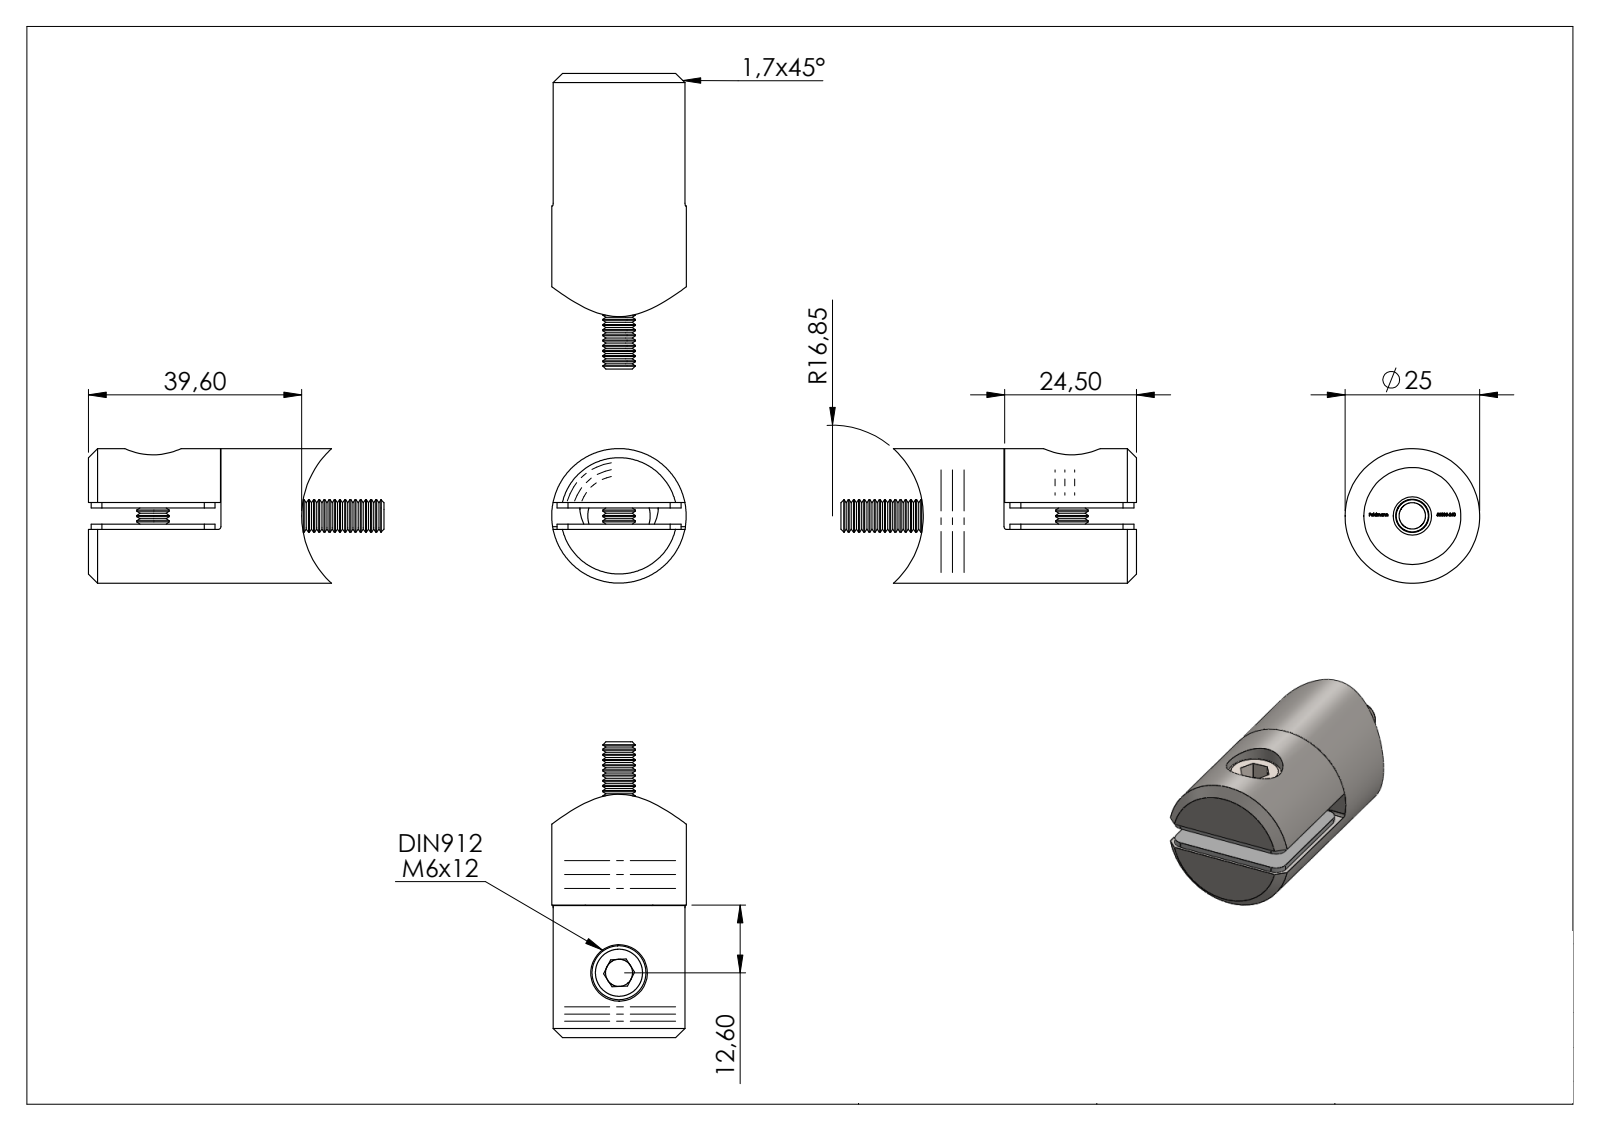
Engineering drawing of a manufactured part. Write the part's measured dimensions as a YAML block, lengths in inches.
part_name: "socket countersunk head screw_din; 55335-240; socket countersunk head screw_din_DIN 7991 - M6 x 25 --- 25S; 5533X-240 Teil1 (+7 more)"
step_written_by: "SolidWorks 2018 (CONFIG_CONTROL_DESIGN)"
units: inches
bodies: {solids: 6, faces: 716, planar: 214, cylindrical: 187, other: 315}
overall_size: [2.161, 0.984, 0.984]
volume: 0.949
surface_area: 16.49
round_holes:
  - {diameter: 0.157, count: 2}
  - {diameter: 0.197, count: 1}
  - {diameter: 0.256, count: 1}
  - {diameter: 0.276, count: 1}
  - {diameter: 0.28, count: 1}
  - {diameter: 0.413, count: 1}
  - {diameter: 0.575, count: 1}
  - {diameter: 0.709, count: 1}
round_bosses_or_shafts:
  - {diameter: 0.236, count: 2}
  - {diameter: 0.984, count: 1}
  - {diameter: 0.456, count: 1}
  - {diameter: 0.394, count: 1}
partial_cylinders:
  - {radius: 0.008, count: 40}
  - {radius: 0.079, count: 6}
  - {radius: 0.049, count: 2}
  - {radius: 0.02, count: 1}
  - {radius: 0.663, count: 1}
face_to_face_distances: [0.157, 0.039, 0.197, 0.118, 1.358, 0.394, 0.965, 0.236, 0.39, 0.969]
hole_center_spacings: [0.369, 0.472]
